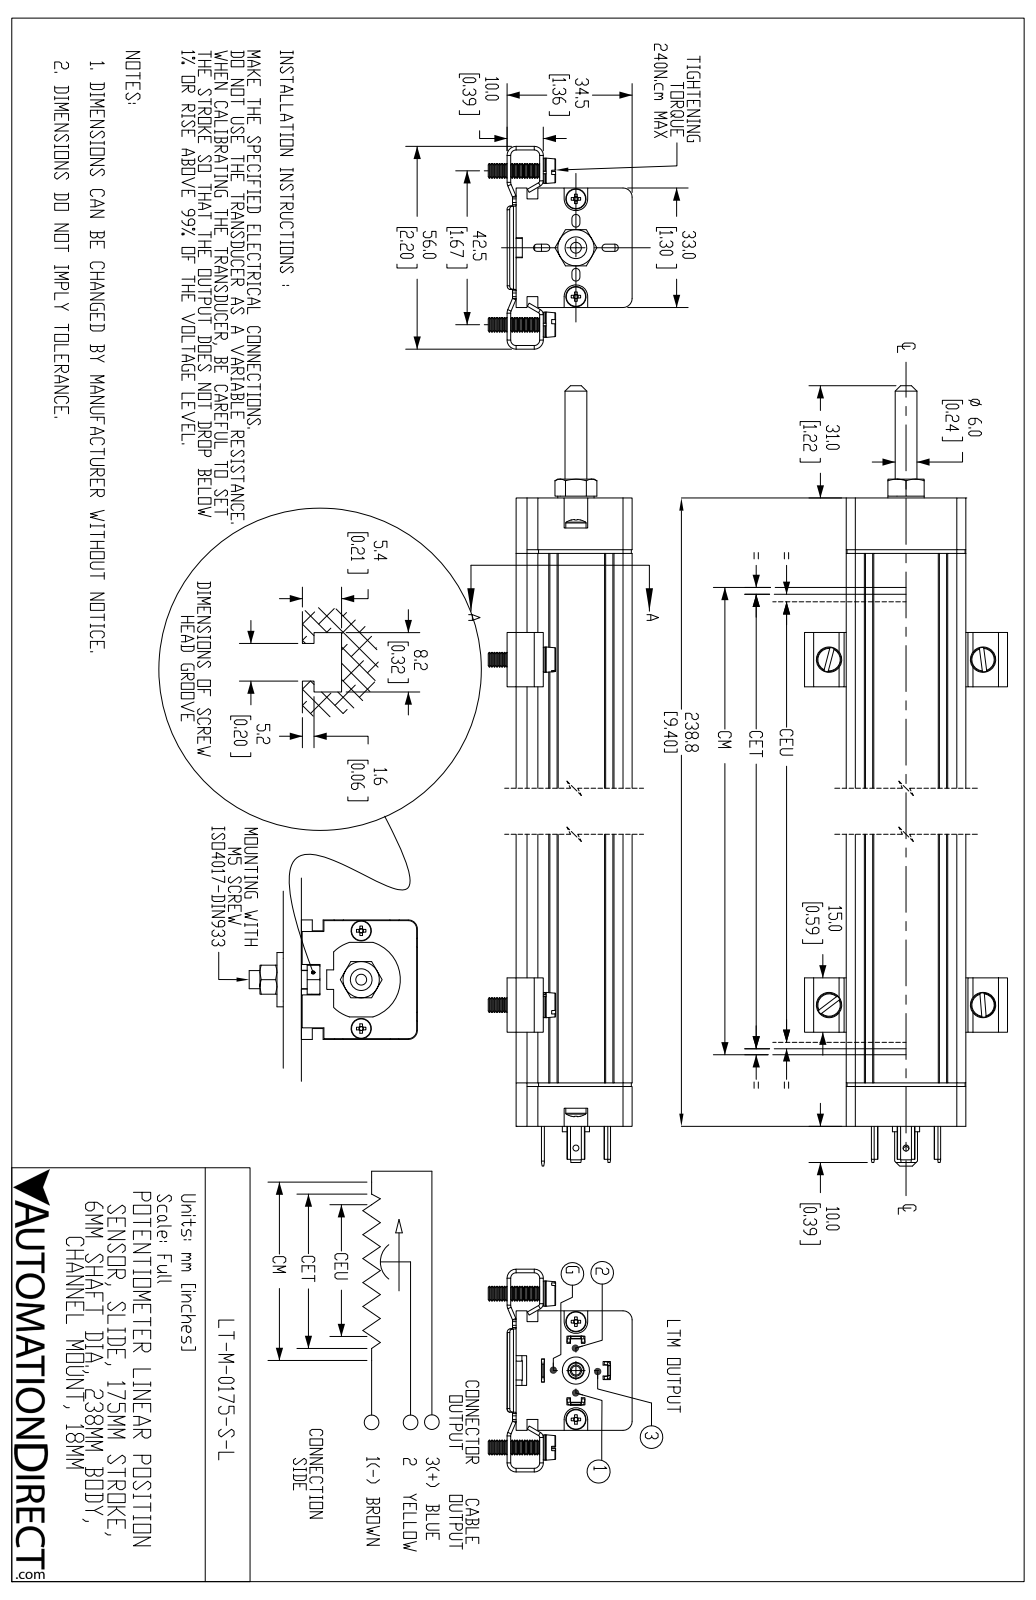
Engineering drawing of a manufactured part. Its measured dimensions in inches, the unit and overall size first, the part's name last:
Units: inches
Overall size (bounding box): 11.749 × 2.205 × 1.563
Round holes (diameter × count): ⌀0.142 ×4, ⌀0.059 ×2, ⌀0.065 ×2, ⌀0.108 ×2, ⌀0.134 ×2, ⌀0.169 ×2, ⌀0.063 ×1, ⌀0.098 ×1, ⌀0.118 ×1, ⌀0.163 ×1, ⌀0.197 ×1, ⌀0.276 ×1
Round bosses / shafts (diameter × count): ⌀0.274 ×4, ⌀0.157 ×4, ⌀0.22 ×2, ⌀0.118 ×2, ⌀0.295 ×1, ⌀0.236 ×1, ⌀0.177 ×1, ⌀0.173 ×1
Partial cylindrical surfaces — rounded edges, fillets, slot ends (radius × count): R0.039 ×34, R0.098 ×12, R0.059 ×10, R0.085 ×8, R0.033 ×6, R0.043 ×4, R0.024 ×2, R0.063 ×2
Main face-to-face distances: 1.299, 1.26, 0.118, 0.039, 1.287, 0.213, 0.059, 0.488, 1.047, 1.024
Hole centre spacings: 0.484, 0.531, 1.359, 1.663, 1.673, 1.766, 1.78, 6.764
Volume: 14.88 in³ · Surface area: 96 in²
Bodies: 21 solids, 1620 faces (696 planar, 356 cylindrical, 568 other)
Part name (STEP PRODUCT): LT-M-0175-S-L
STEP written by: SolidWorks 2019 (AUTOMOTIVE_DESIGN)
